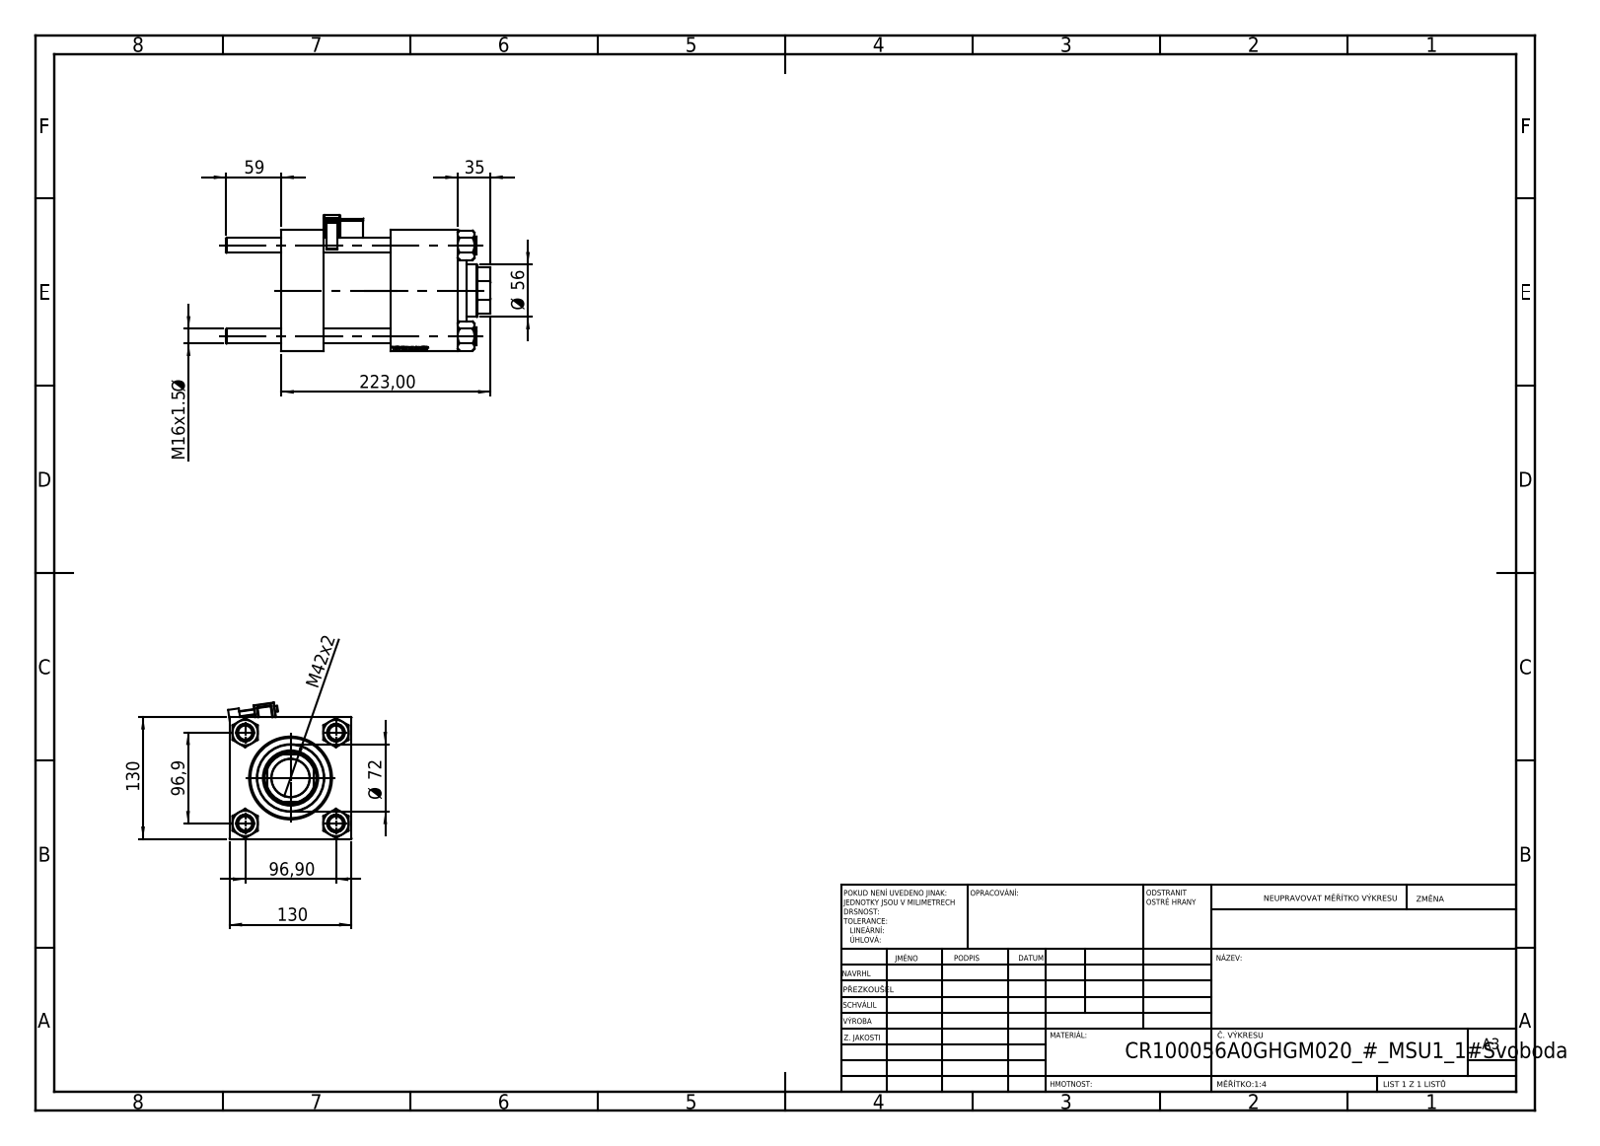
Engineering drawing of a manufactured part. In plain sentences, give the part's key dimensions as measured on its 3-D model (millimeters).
The part is named "CR025_012_A_0_G_A_G_M_020_+#_##_TYCINKA; V215CR_VCP; V215_VC_A; V215CR_BODY_A (+2 more)". Its 3-D file was written by "SolidWorks 2019 (CONFIG_CONTROL_DESIGN)". It is 12 solids with 1259 faces: 597 planar, 108 cylindrical and 554 other. Overall it measures 282 by 145.5 by 131.61 millimeters. Its volume is 2 576 000 cubic millimeters and its surface area 366 819 square millimeters. Round holes: 4 of diameter 16, 2 of diameter 7, 2 of diameter 26.44, 2 of diameter 35, 1 of diameter 40.5, 1 of diameter 56, 1 of diameter 59, 1 of diameter 76, 1 of diameter 85.5, 1 of diameter 100. Round bosses or shafts: 4 of diameter 19, 1 of diameter 106, 1 of diameter 72, 1 of diameter 6. Partial cylindrical surfaces (rounded edges, fillets, slot ends): 24 of radius 0.5, 1 of radius 1, 1 of radius 2.5, 1 of radius 4, 1 of radius 27. The main face-to-face distances are 130, 45, 188, 143, 116, 71, 72, 20, 92, 96. The hole center spacings are 68.52, 96.9, 137.04, 118.5.
